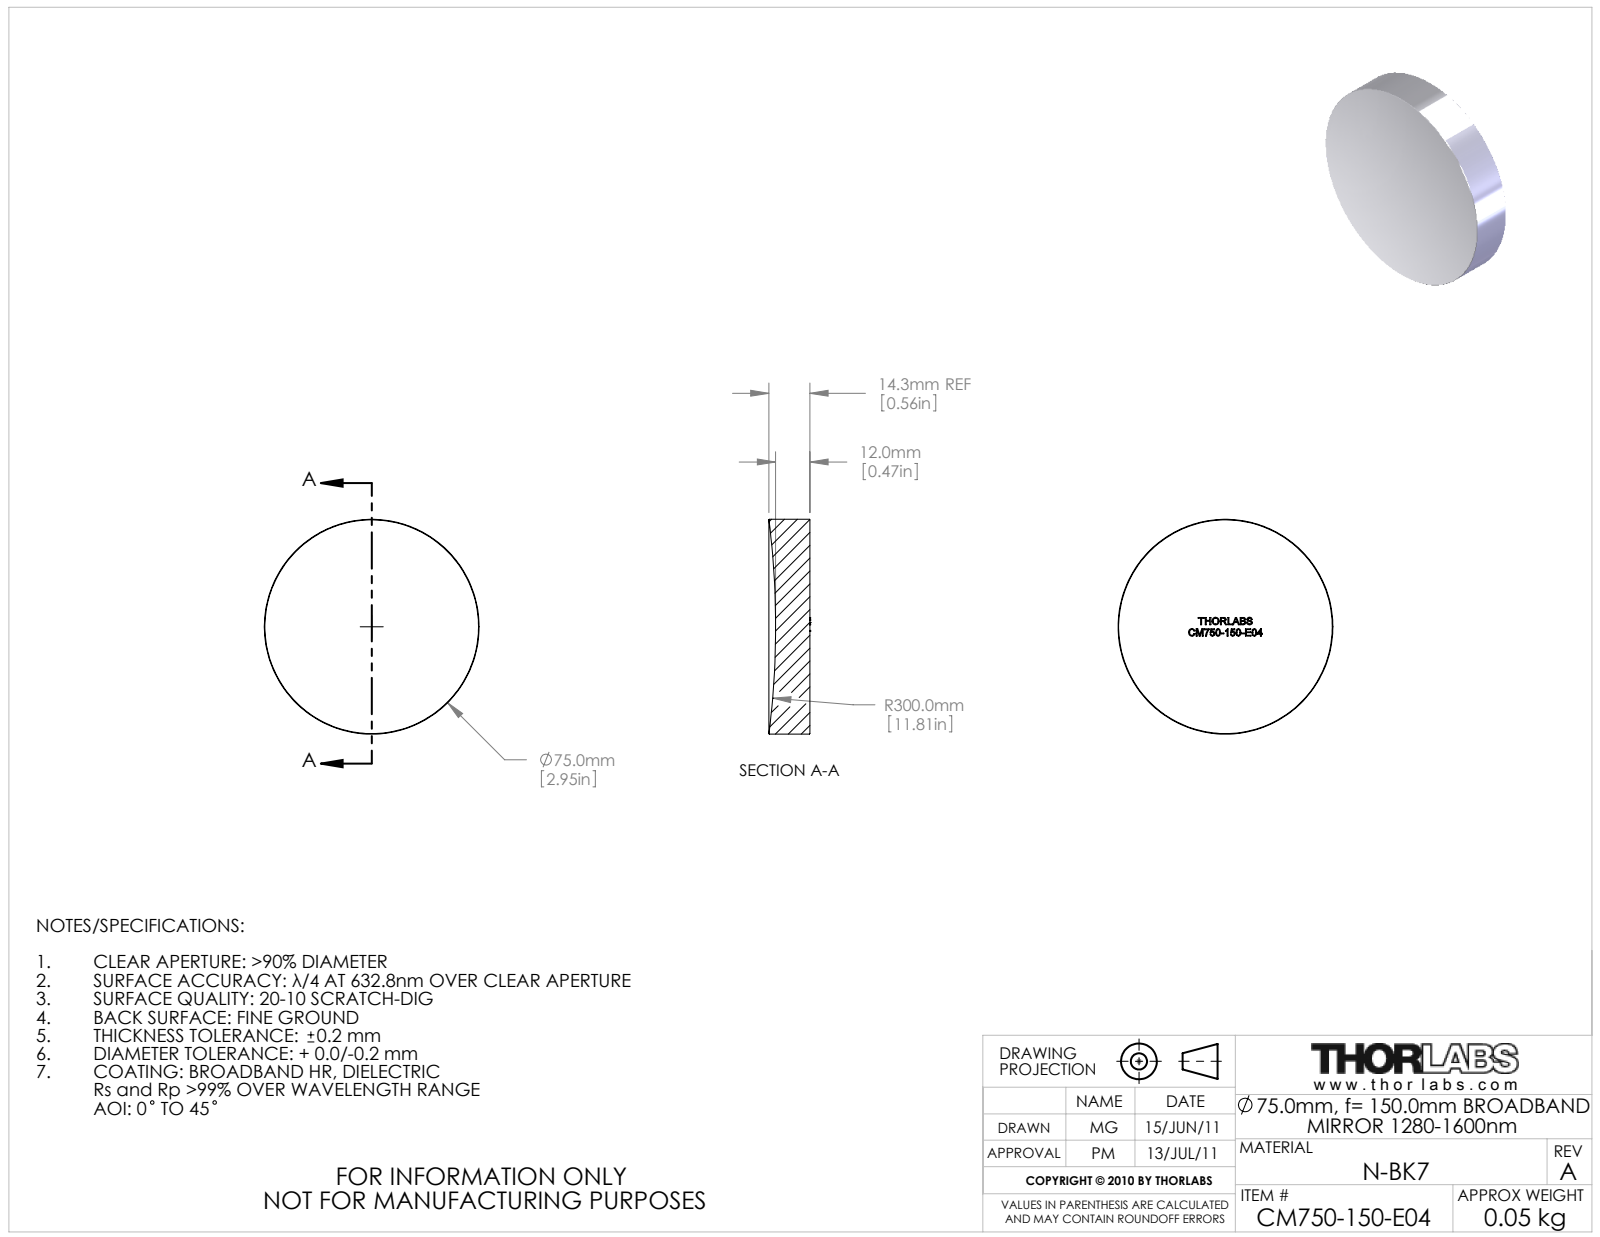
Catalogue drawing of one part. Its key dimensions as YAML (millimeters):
part_name: "22665-E0W"
step_written_by: "SolidWorks 2011 (AUTOMOTIVE_DESIGN)"
units: millimeters
bodies: {solids: 0, faces: 40, planar: 32, cylindrical: 2, other: 6}
overall_size: [75, 75, 14.33]
round_bosses_or_shafts:
  - {diameter: 75, count: 1}
